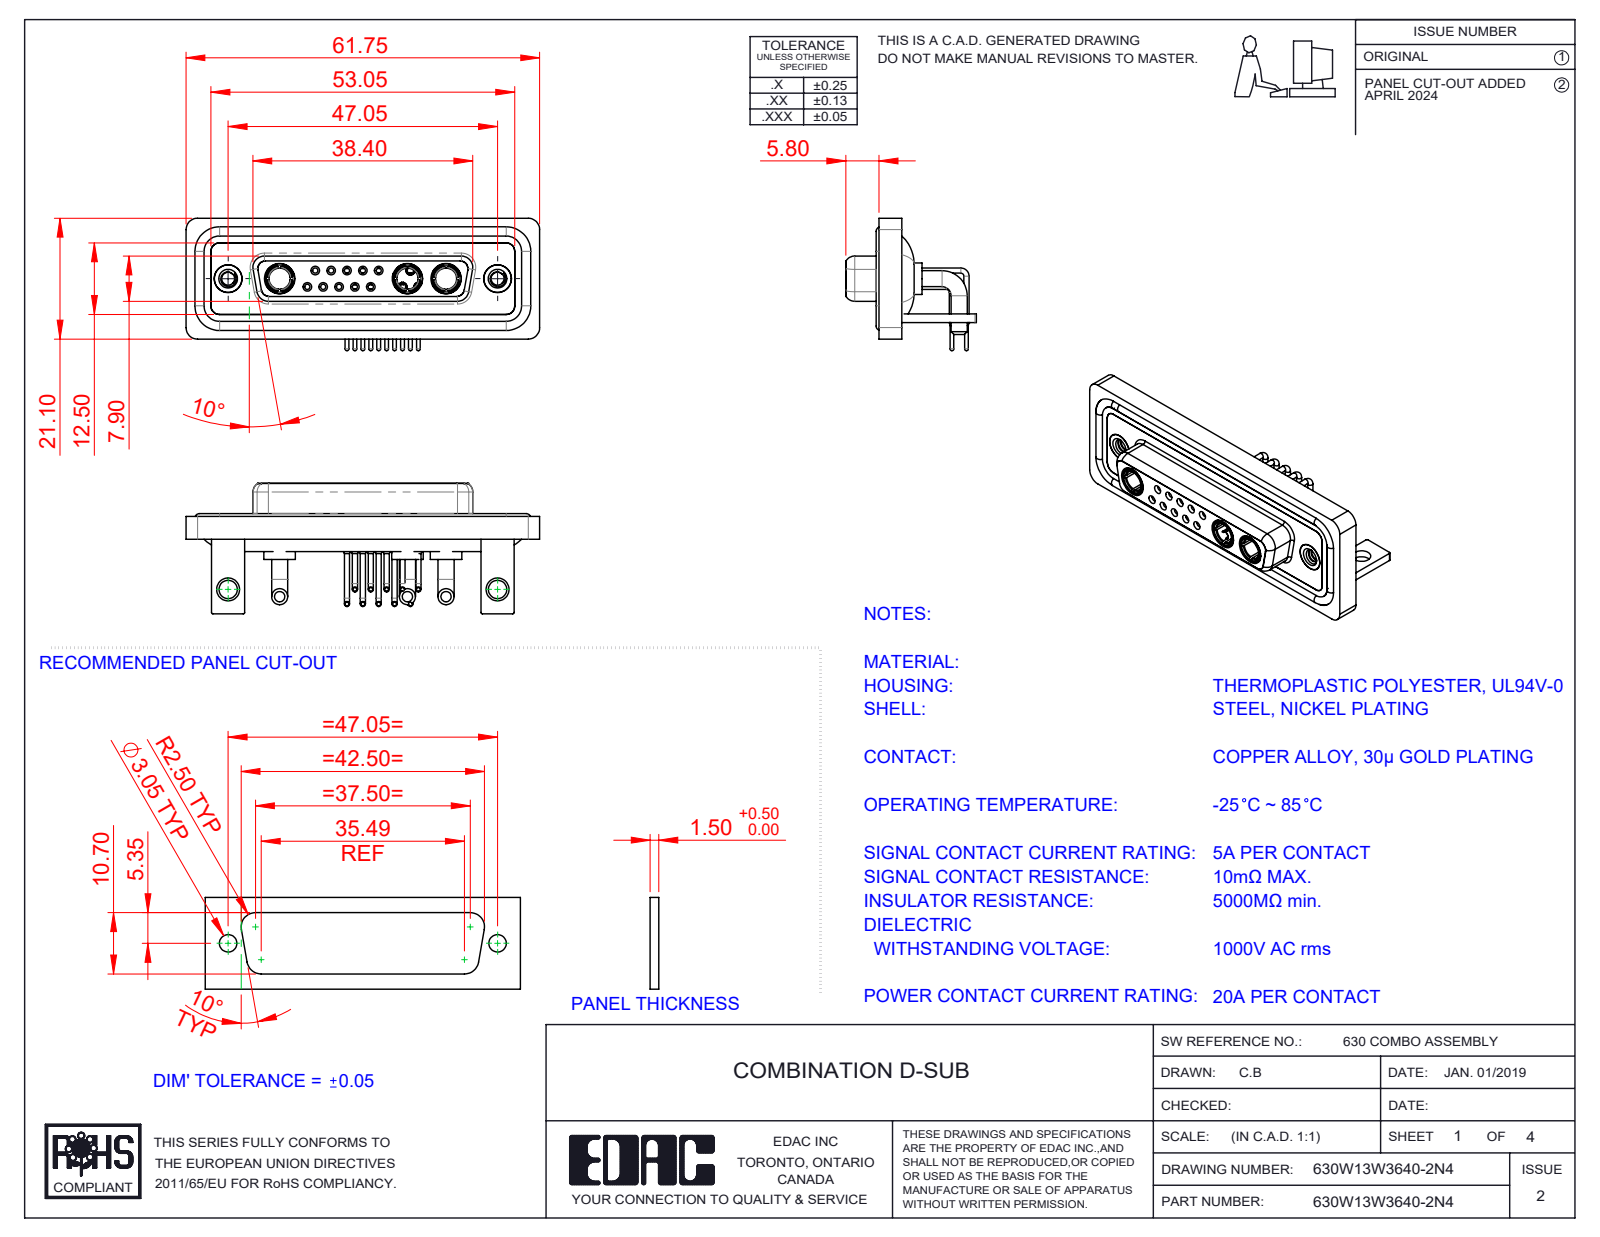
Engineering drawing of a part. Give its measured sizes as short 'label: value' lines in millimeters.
name: 630W13W3640-2N4; 630Combo Shell Front_25 Contacts; 630Combo Threaded Rivet_2; 630Combo Housing_13W3 (+6 more)
written by: SolidWorks 2023 (CONFIG_CONTROL_DESIGN)
unit: mm
bodies: 25 solids, 1198 faces (362 planar, 517 cylindrical, 319 other)
size: 61.75 × 23.12 × 22.8
volume: 8 837 mm³; area: 15 032 mm²
holes: 10× ⌀0.9, 10× ⌀1.1, 10× ⌀1.5, 10× ⌀2, 5× ⌀1.6, 5× ⌀1.7, 5× ⌀4.85, 3× ⌀3.7, 3× ⌀5.3, 2× ⌀2.26, 2× ⌀3.2, 2× ⌀4
bosses: 15× ⌀0.9, 12× ⌀1.6, 10× ⌀0.65, 6× ⌀2.8, 5× ⌀2, 5× ⌀1.5, 3× ⌀5.5, 3× ⌀5.2
rounds: 19× R2, 18× R1.5, 16× R0.25, 8× R1.35, 8× R1.6, 5× R0.5, 4× R0.6, 4× R0.65
face distances: 0.4, 1.8, 2.9, 3.7, 1.5, 4.1, 1.1, 1.4, 1.6, 3.1
hole spacings: 3.16, 2.77, 5.54, 5.04, 8.31, 5.03, 7.49, 11.08
